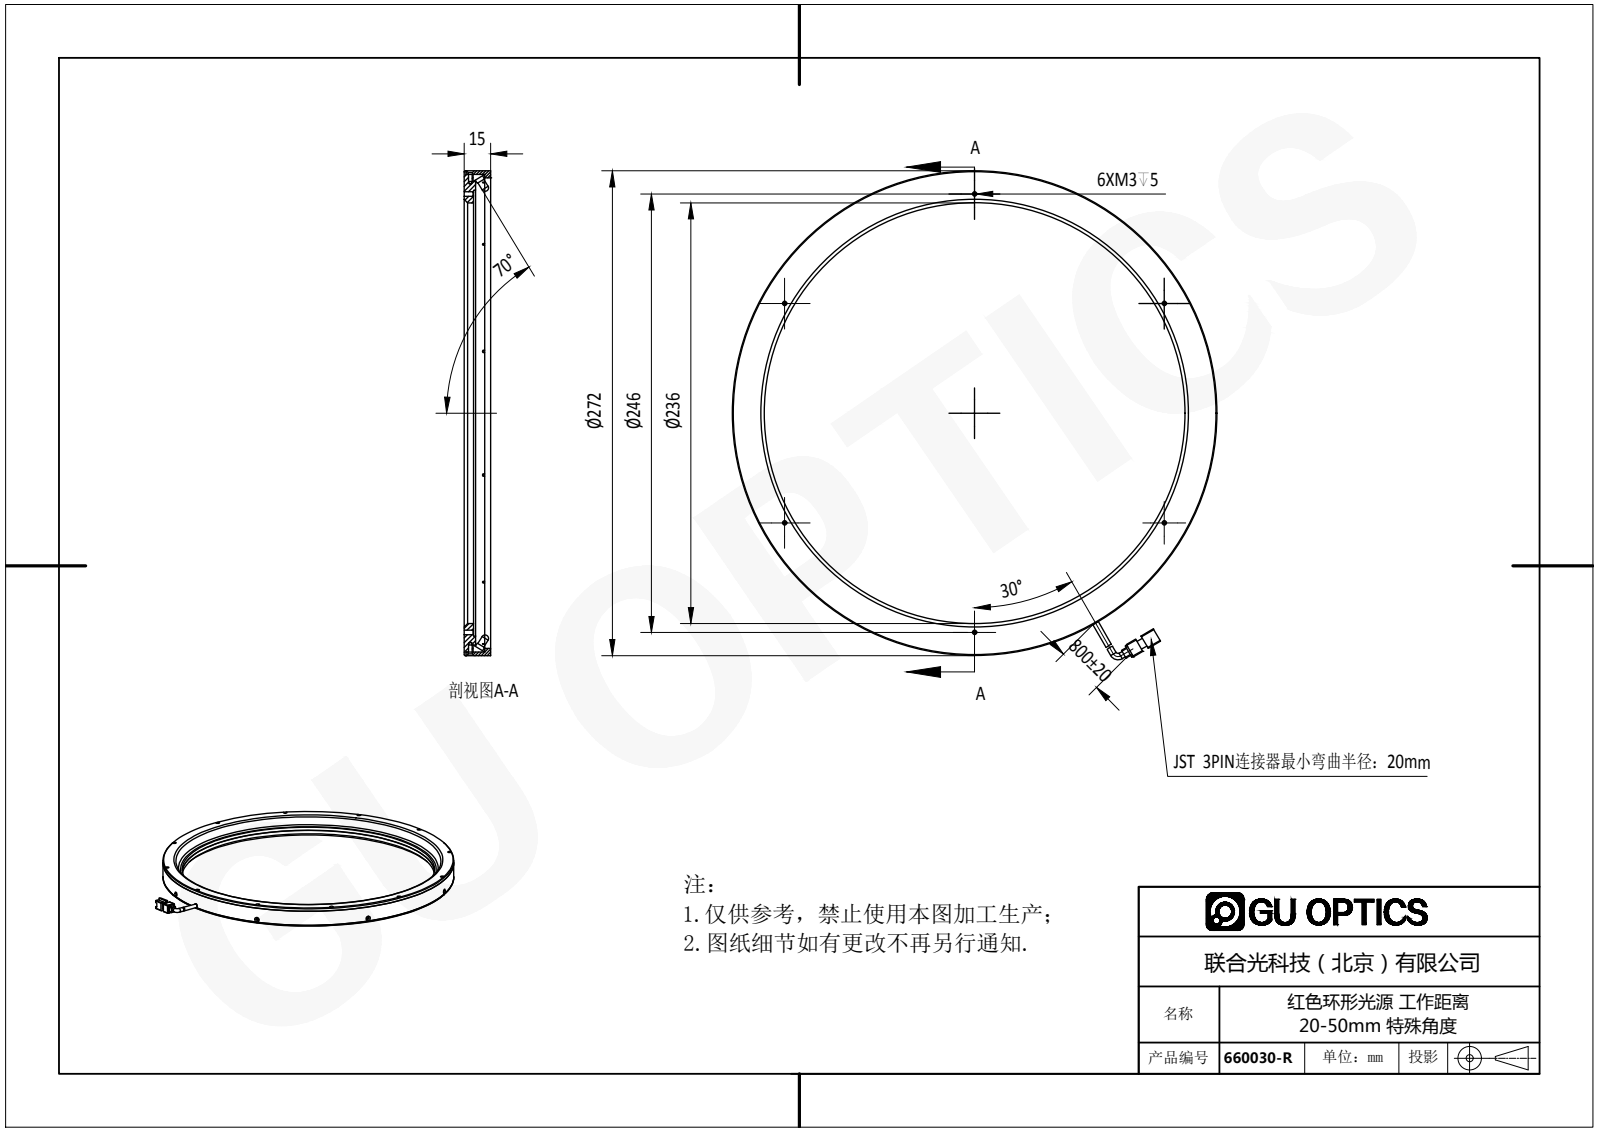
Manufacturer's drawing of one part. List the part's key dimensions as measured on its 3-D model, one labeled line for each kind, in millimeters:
Part name (STEP PRODUCT): 660030-R
STEP written by: SolidWorks 2016 (AUTOMOTIVE_DESIGN)
Units: millimetres
Bodies: 156 solids, 2958 faces (1895 planar, 793 cylindrical, 270 other)
Overall size (bounding box): 274.35 × 272 × 19.24
Volume: 168 197 mm³ · Surface area: 140 450 mm²
Round holes (diameter × count): ⌀1.6 ×18, ⌀1.25 ×12, ⌀1.7 ×12, ⌀2 ×6, ⌀2.4 ×6, ⌀2.5 ×6, ⌀3.5 ×1, ⌀236 ×1, ⌀250 ×1, ⌀264 ×1
Round bosses / shafts (diameter × count): ⌀3.8 ×150, ⌀3 ×150, ⌀3.5 ×2, ⌀272 ×1, ⌀268 ×1, ⌀260 ×1
Partial cylindrical surfaces — rounded edges, fillets, slot ends (radius × count): R0.5 ×8, R1 ×4, R1.6 ×1, R3 ×1
Main face-to-face distances: 14.94, 3, 17.94, 5.3, 9.64, 12.64, 6.5, 8.44, 1, 1.2
Hole centre spacings: 134, 34.98, 163.15, 247.6, 265.71, 69.36, 102.56, 258.87
